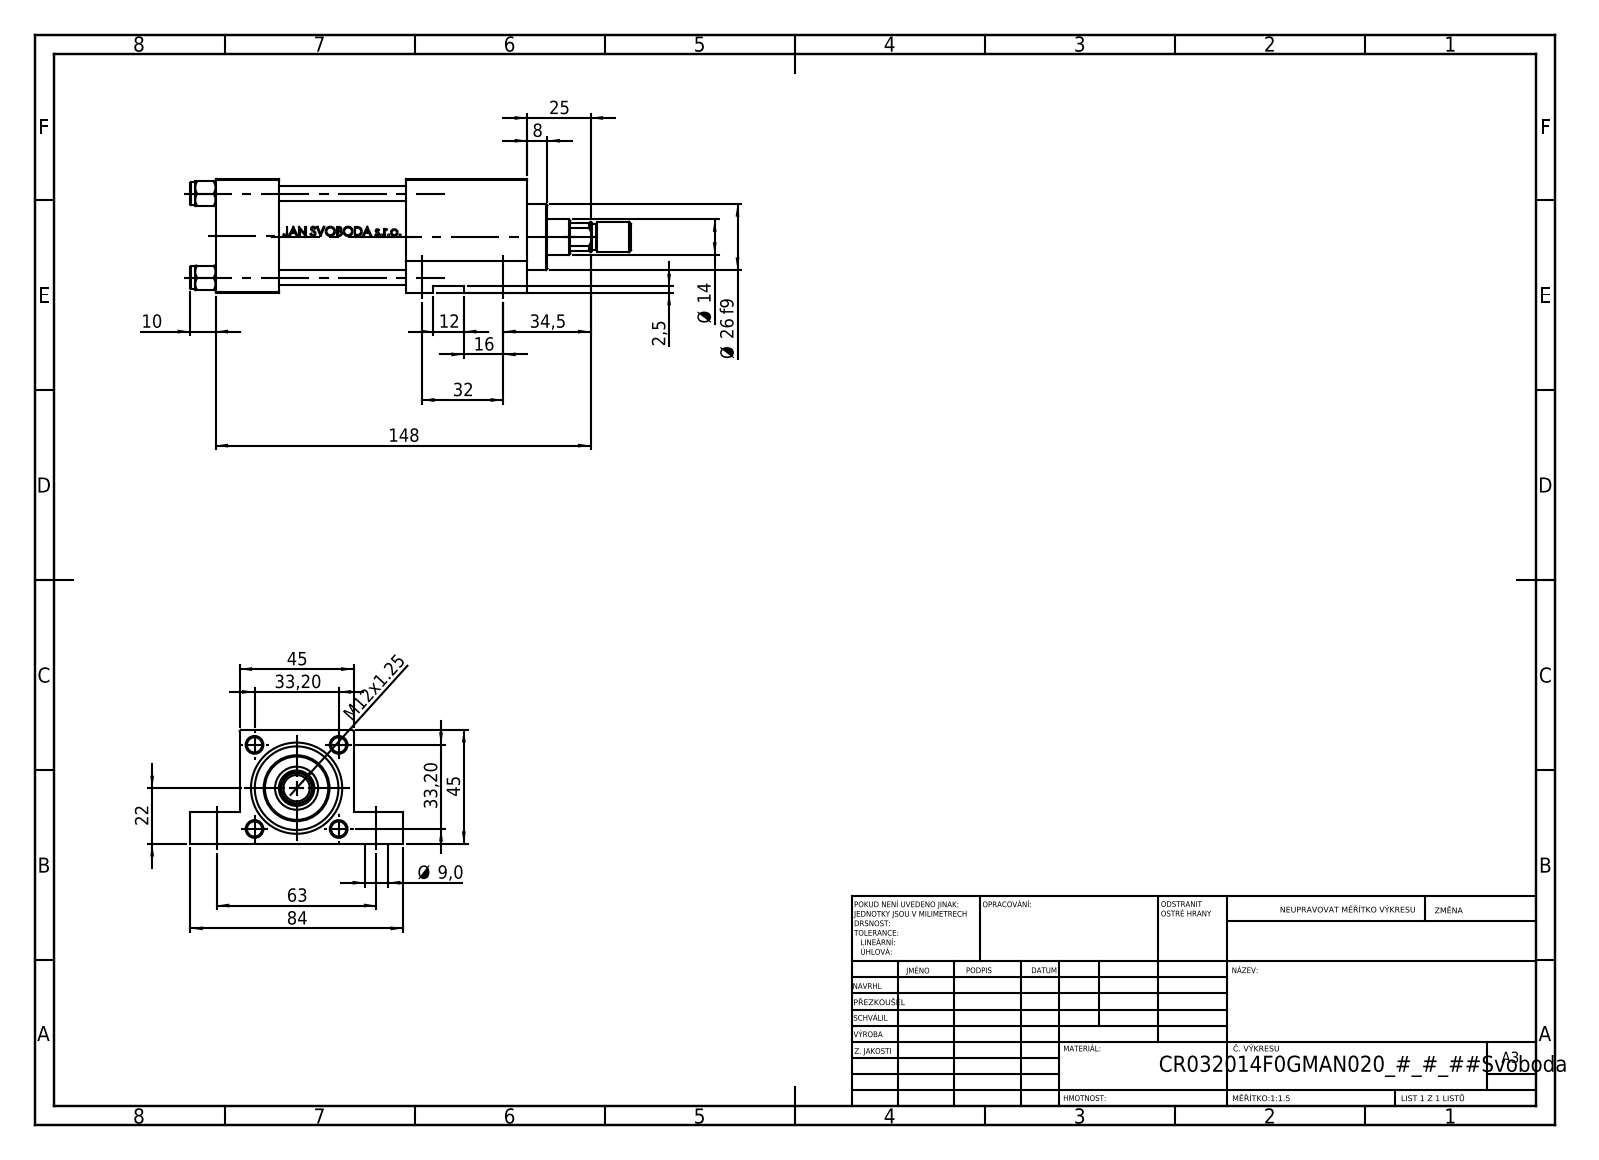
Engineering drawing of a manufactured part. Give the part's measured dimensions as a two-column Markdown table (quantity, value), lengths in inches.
| quantity | value |
| --- | --- |
| part name | NUT_M5_F; V215CR_F_Body; V215_VC_A; V215CR_VCP_F (+2 more) |
| STEP written by | SolidWorks 2019 (CONFIG_CONTROL_DESIGN) |
| units | inches |
| bodies | 12 solids, 1116 faces (440 planar, 130 cylindrical, 546 other) |
| overall size | 6.85 × 3.307 × 1.772 |
| volume | 13.04 in³ |
| surface area | 114 in² |
| round holes (diameter × count) | 0.236 × 4, 0.354 × 4, 0.276 × 2, 0.787 × 2, 0.256 × 1, 0.512 × 1, 0.518 × 1, 0.551 × 1, 0.669 × 1, 0.945 × 1, 1.26 × 1, 1.299 × 1 |
| round bosses / shafts (diameter × count) | 0.354 × 4, 1.496 × 1, 1.024 × 1, 0.472 × 1, 0.394 × 1 |
| partial cylindrical surfaces (radius × count) | 0.256 × 1 |
| main face-to-face distances | 1.772, 0.984, 3.858, 4.843, 1.969, 1.28, 2.953, 1.89, 0.492, 0.394 |
| hole center spacings | 1.307, 0.911, 0.938, 1.26, 1.848, 2.48, 2.782, 2.972 |
